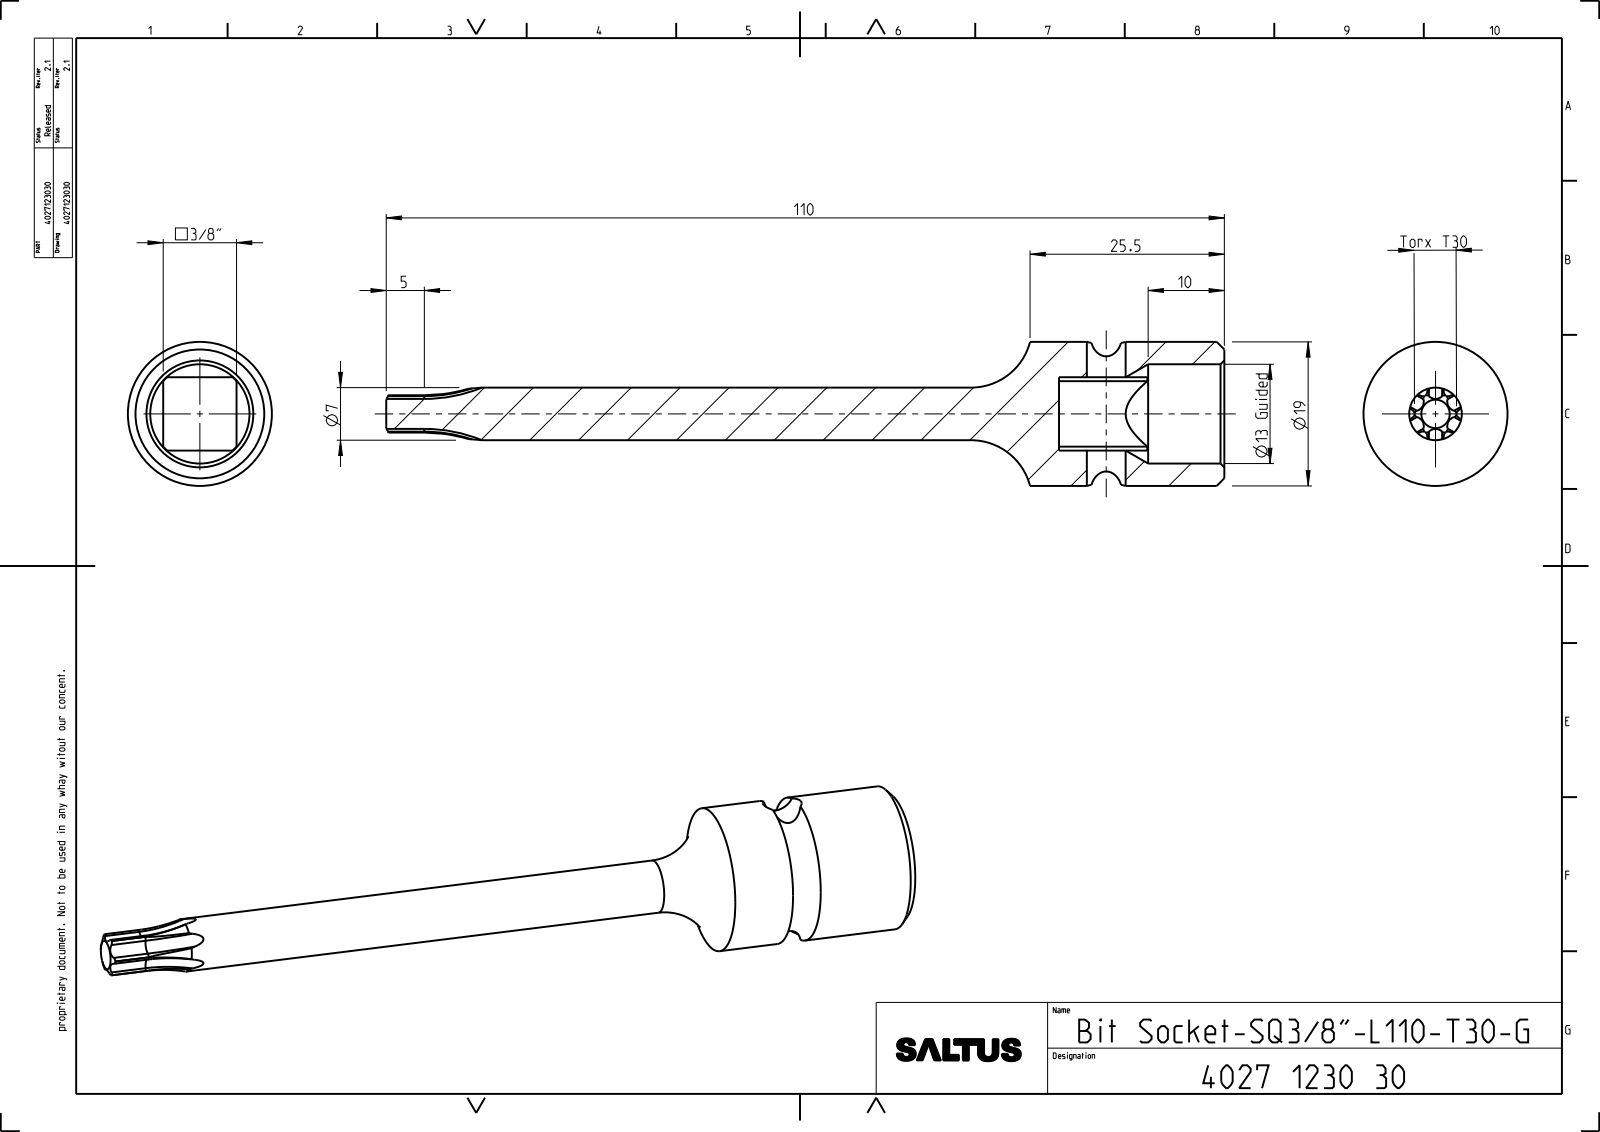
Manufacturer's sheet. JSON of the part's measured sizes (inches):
{"part_name": "4027123030", "step_written_by": "CREO PARAMETRIC BY PTC INC, 2022414 (CONFIG_CONTROL_DESIGN)", "units": "inches", "bodies": {"solids": 1, "faces": 83, "planar": 7, "cylindrical": 40, "other": 36}, "overall_size": [4.331, 0.744, 0.744], "volume_in3": 0.465, "surface_area_in2": 7.239, "round_holes": [[0.2, 1], [0.513, 1]], "round_bosses_or_shafts": [[0.744, 1], [0.272, 1]], "partial_cylinders_radius": [[0.017, 12], [0.048, 6], [0.109, 1], [0.254, 1]], "face_to_face_distances": [0.379, 0.854, 4.331, 3.476]}
